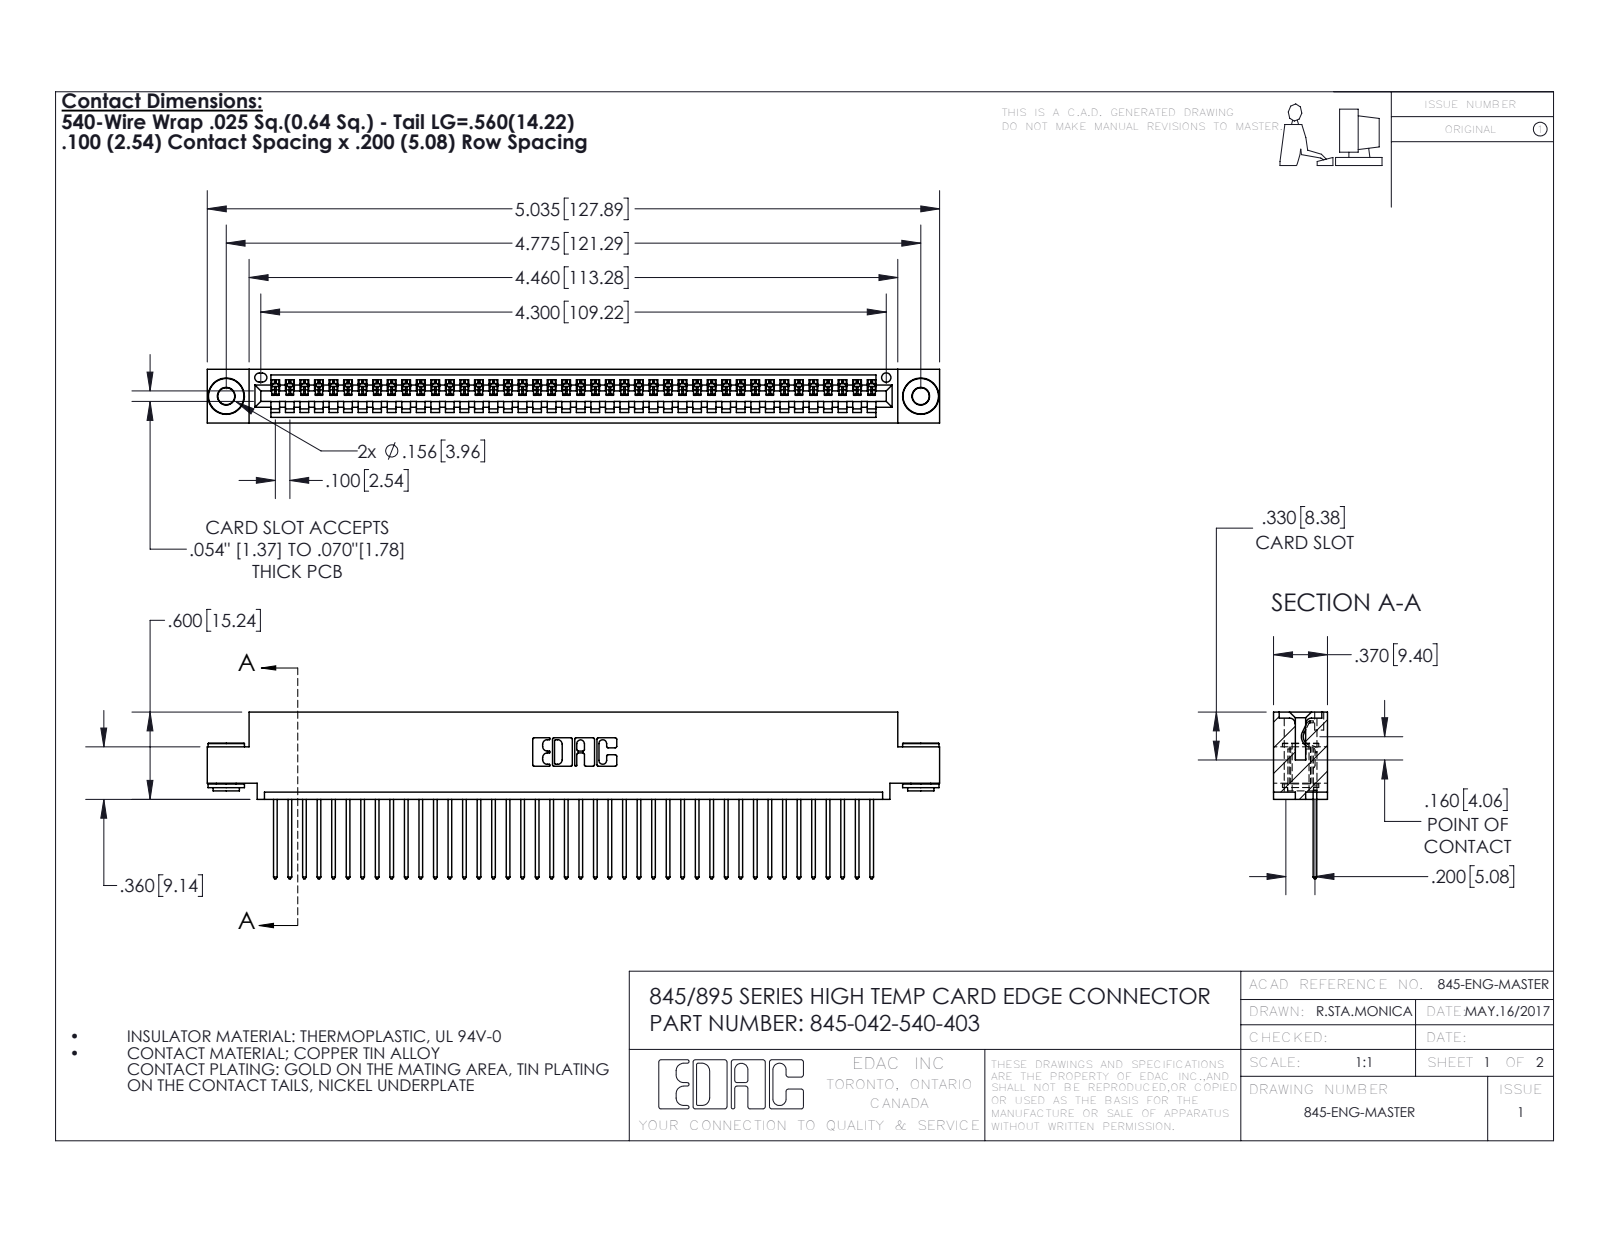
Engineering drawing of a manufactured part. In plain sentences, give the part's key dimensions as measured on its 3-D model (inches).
The part is named "345 Part_0.110 Offset - 0.156 Dia-TH; 345-292-001_345-293-140; 345-042-540-403; 345-250-002_345-250-002-102". Its 3-D file was written by "SolidWorks 2016 (CONFIG_CONTROL_DESIGN)". It is 45 solids with 2604 faces: 1774 planar, 822 cylindrical and 8 other. Overall it measures 5.035 by 1.147 by 0.37 inches. Its volume is 0.741 cubic inches and its surface area 26.12 square inches. Round holes: 2 of diameter 0.116, 2 of diameter 0.156, 1 of diameter 0.064. Round bosses or shafts: 2 of diameter 0.25, 2 of diameter 0.18, 2 of diameter 0.136. Partial cylindrical surfaces (rounded edges, fillets, slot ends): 84 of radius 0.006, 84 of radius 0.01, 22 of radius 0.01, 6 of radius 0.007, 6 of radius 0.031, 3 of radius 0.026, 2 of radius 0.031, 2 of radius 0.04. The main face-to-face distances are 0.072, 0.298, 0.025, 0.37, 0.098, 0.272, 0.2, 0.225, 0.149, 0.072. The hole center spacings are 0.27, 4.539, 4.775.
